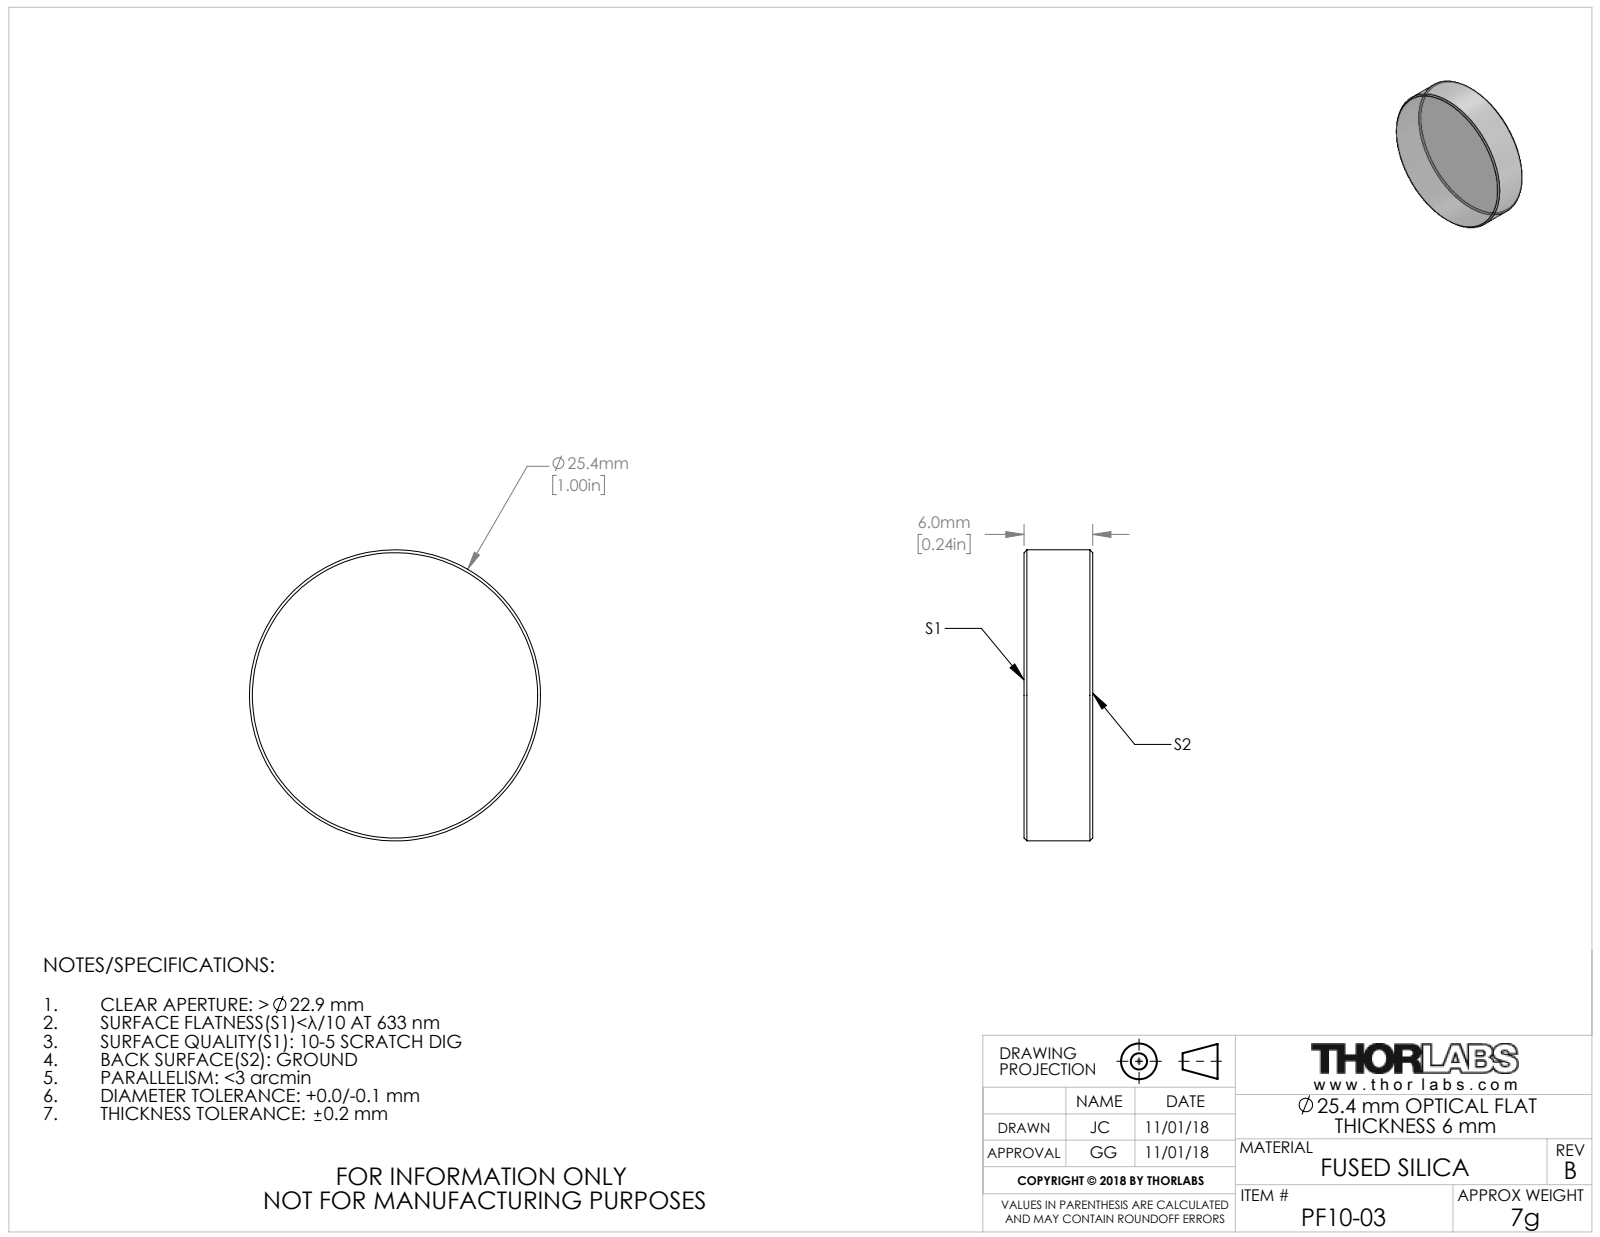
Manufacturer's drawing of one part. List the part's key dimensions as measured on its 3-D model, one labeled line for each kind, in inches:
Part name (STEP PRODUCT): 3592-E0W
STEP written by: SolidWorks 2018 (CONFIG_CONTROL_DESIGN)
Units: inches
Bodies: 1 solid, 8 faces (2 planar, 2 cylindrical, 4 other)
Overall size (bounding box): 1 × 1 × 0.236
Volume: 0.185 in³ · Surface area: 2.277 in²
Round bosses / shafts (diameter × count): ⌀1 ×1
Main face-to-face distances: 0.236
